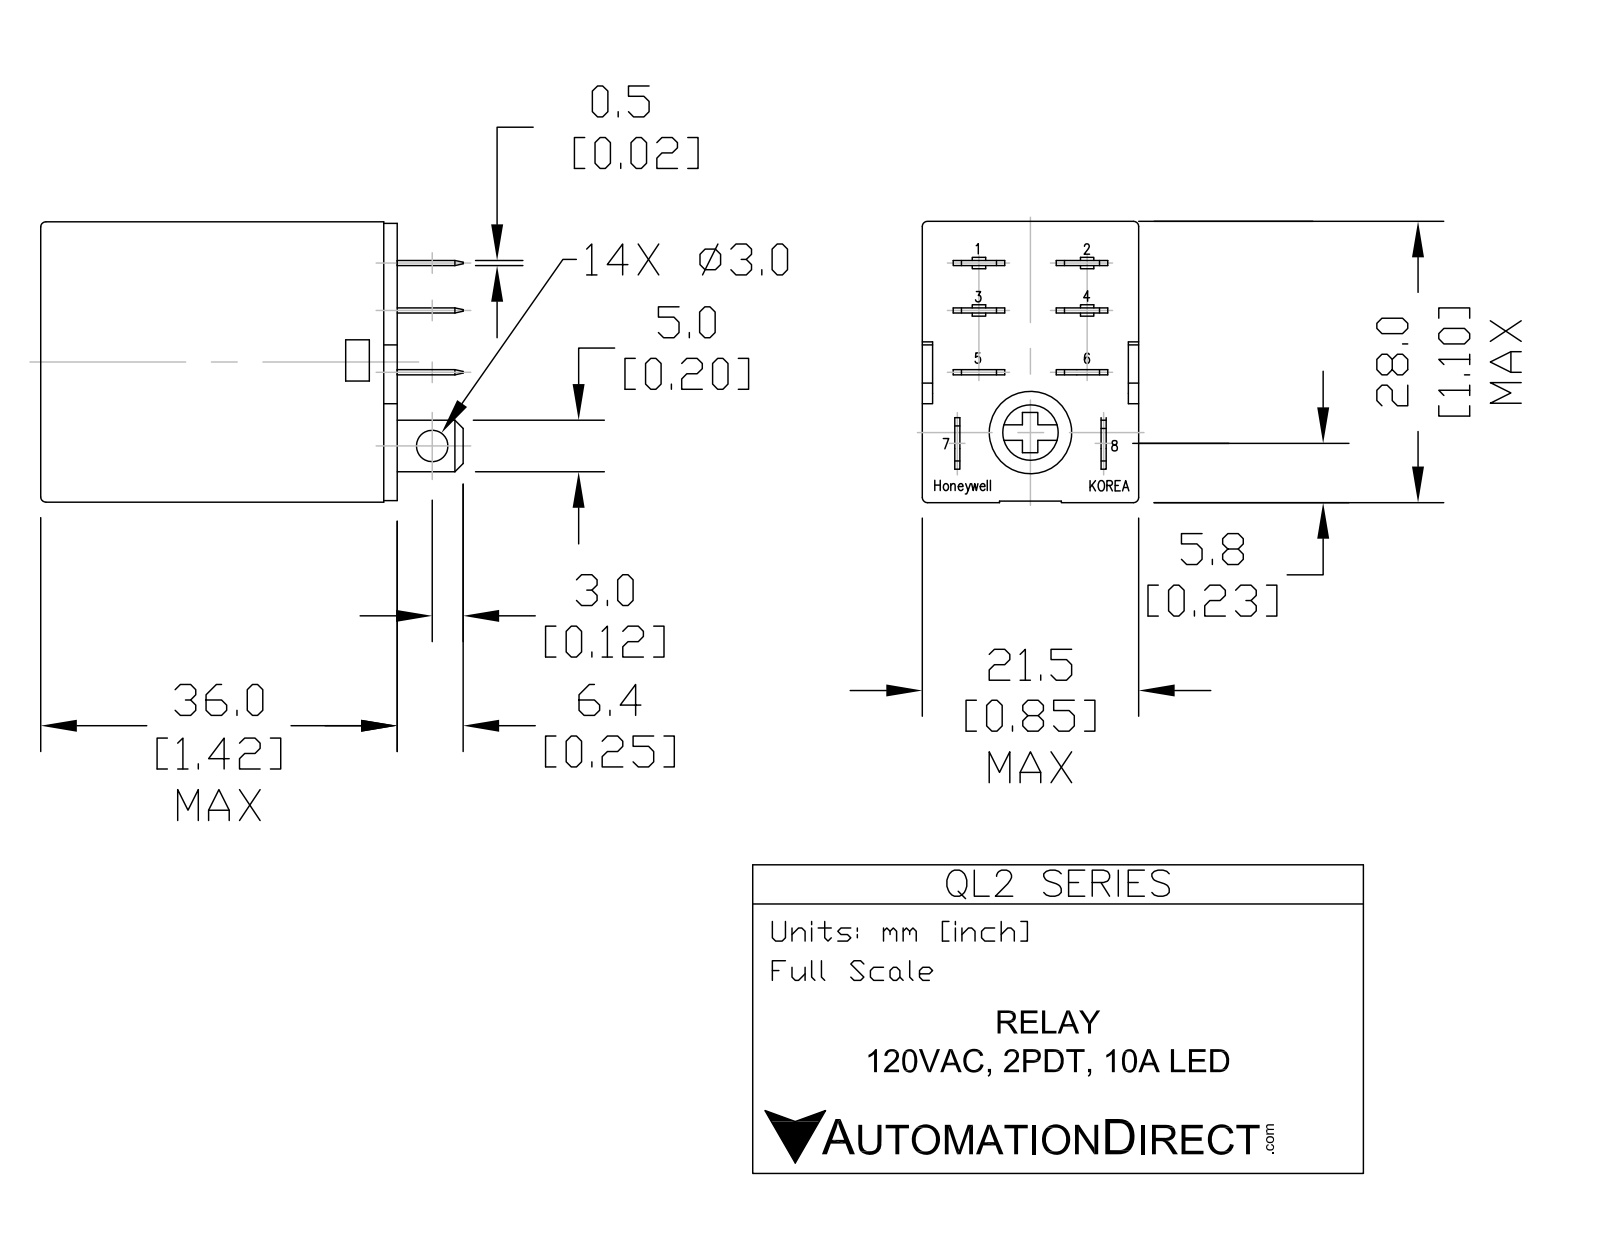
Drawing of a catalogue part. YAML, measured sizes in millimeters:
part_name: "QL2N1-A220"
step_written_by: "SolidWorks 2013 (AUTOMOTIVE_DESIGN)"
units: millimeters
bodies: {solids: 1, faces: 137, planar: 101, cylindrical: 32, other: 4}
overall_size: [42.4, 28, 21.5]
volume: 21148
surface_area: 5075
round_holes:
  - {diameter: 3, count: 3}
  - {diameter: 6.5, count: 1}
round_bosses_or_shafts:
  - {diameter: 4, count: 1}
partial_cylinders:
  - {radius: 1, count: 8}
face_to_face_distances: [36, 0.5, 4.5, 5, 4, 9, 9.5, 8.5, 15, 35.75]
hole_center_spacings: [10.75]
